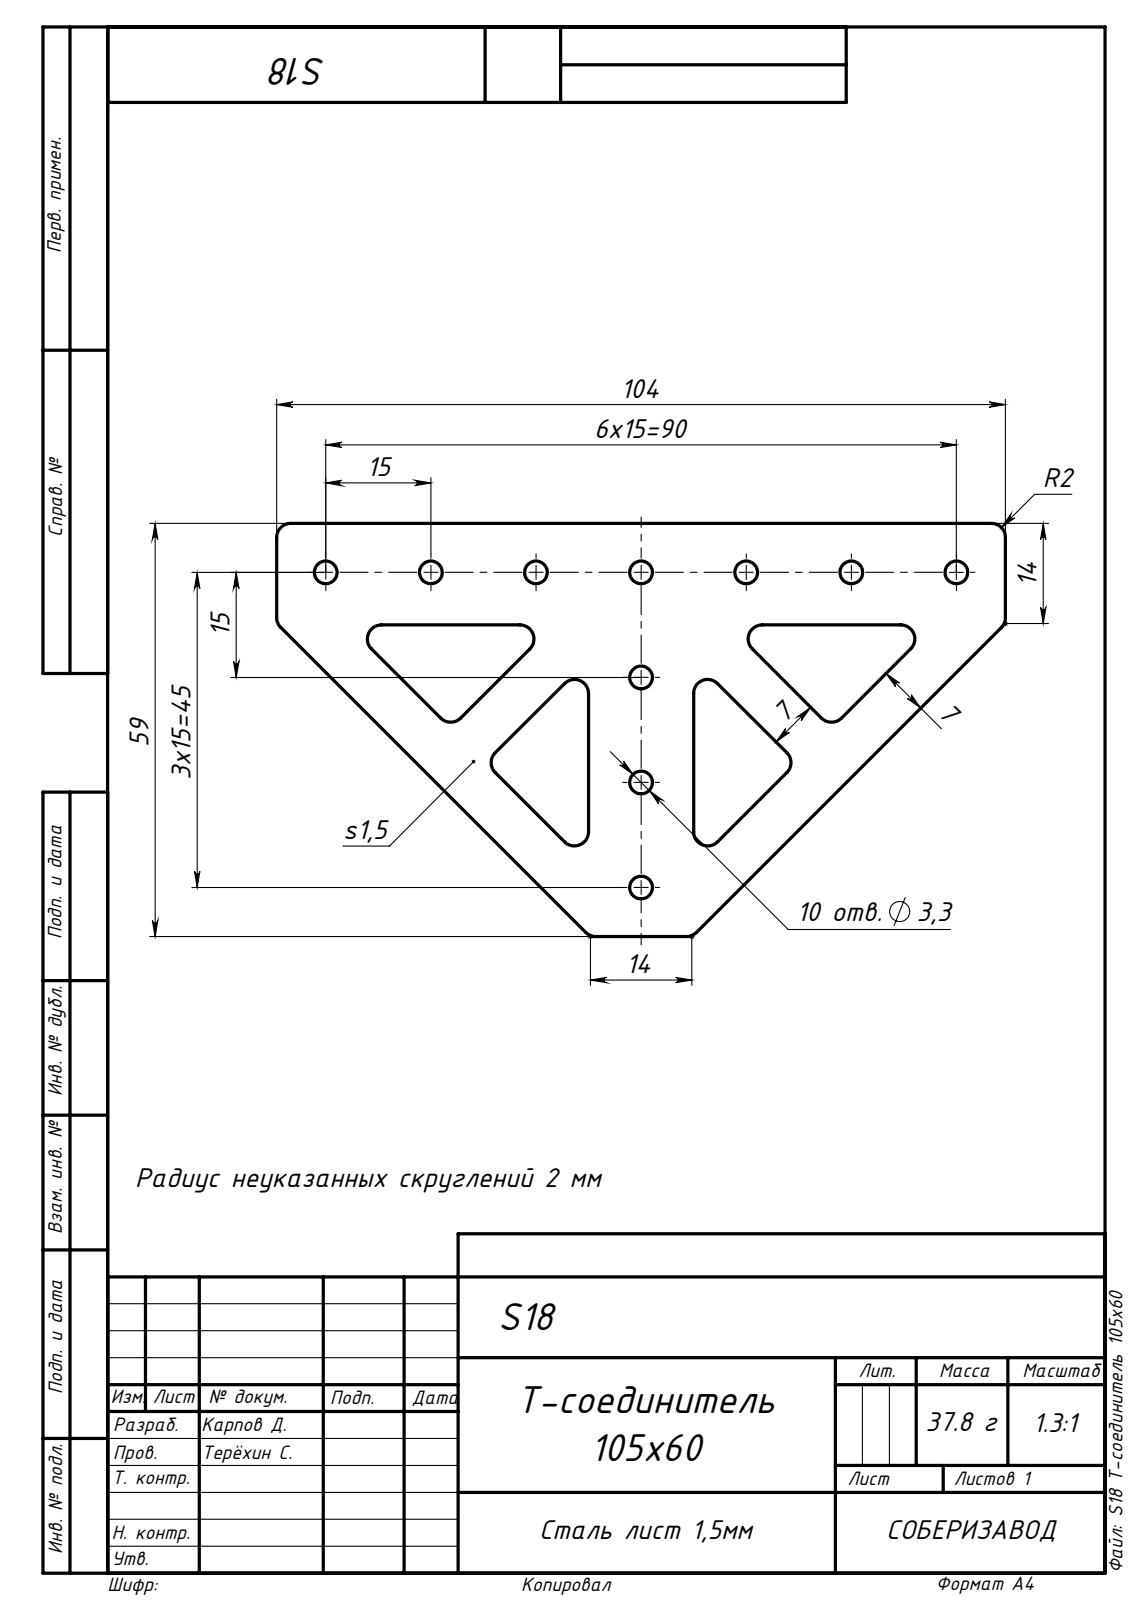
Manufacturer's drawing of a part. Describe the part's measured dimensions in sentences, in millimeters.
The part is named "S18 Т-соединитель 105x60". Its 3-D file was written by "SolidWorks 2019 (AUTOMOTIVE_DESIGN)". It is 1 solid with 60 faces: 20 planar, 40 cylindrical and 0 other. Overall it measures 104 by 59 by 1.5 millimeters. Its volume is 4 842 cubic millimeters and its surface area 7 379 square millimeters. Round holes: 10 of diameter 3.25. Partial cylindrical surfaces (rounded edges, fillets, slot ends): 18 of radius 2. The main face-to-face distances are 1.5, 7, 38.42, 14.5, 44.5, 31.42, 45.42, 59.5, 15, 59. The hole center spacings are 15, 30, 45, 33.54, 47.43, 54.08, 60, 21.21.
